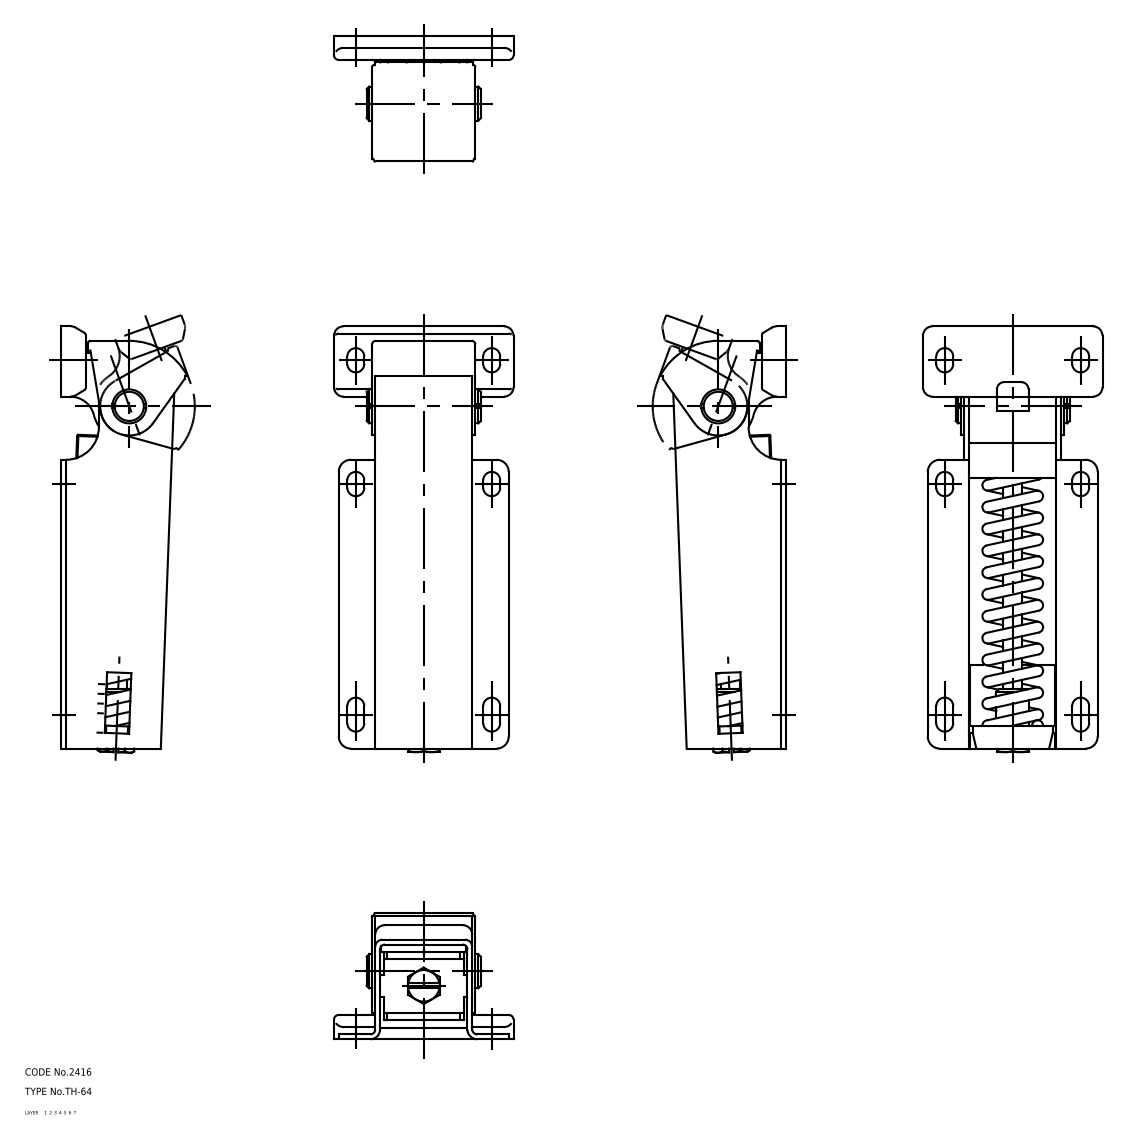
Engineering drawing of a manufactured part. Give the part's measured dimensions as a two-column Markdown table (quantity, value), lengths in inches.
| quantity | value |
| --- | --- |
| part name | set plate; slide; cover_2; spring (+8 more) |
| STEP written by | CADfix (AUTOMOTIVE_DESIGN) |
| units | inches |
| bodies | 11 solids, 243 faces (0 planar, 0 cylindrical, 243 other) |
| overall size | 6.9 × 2.913 × 2.04 |
| volume | 8.125 in³ |
| surface area | 150.2 in² |
